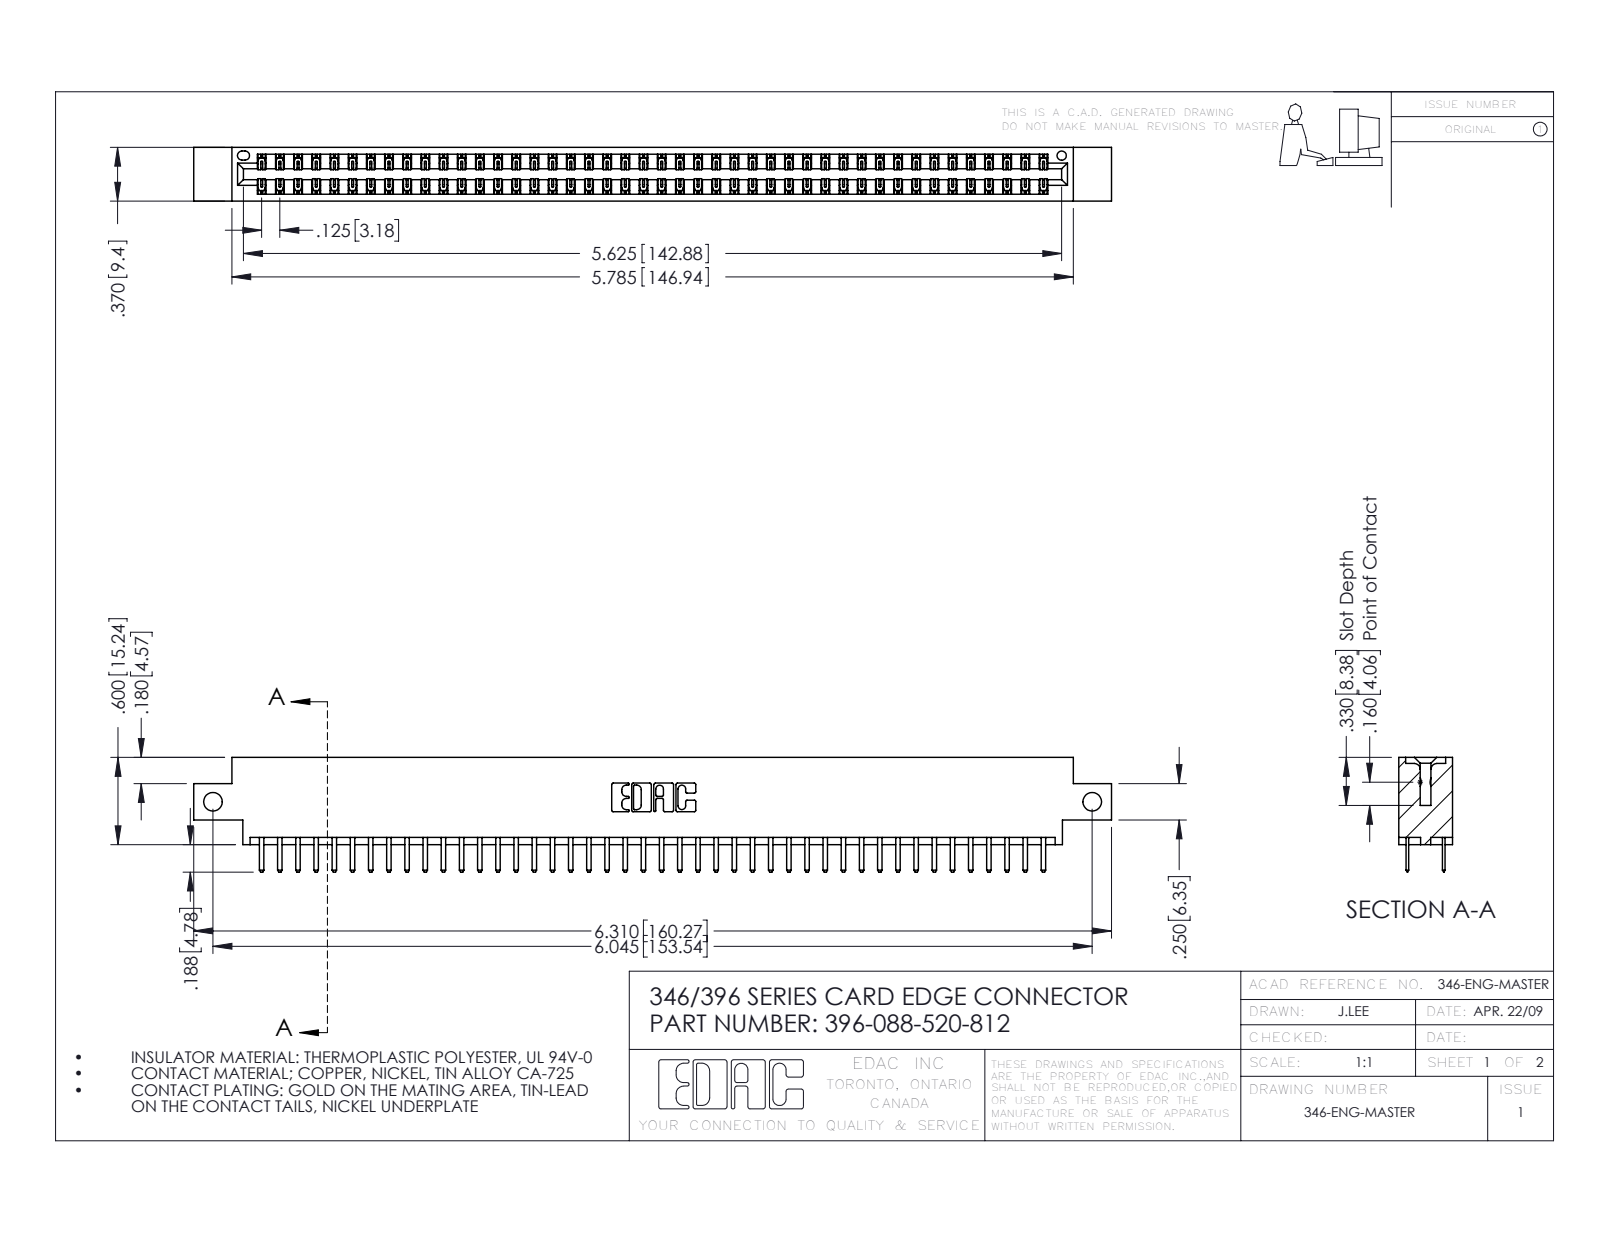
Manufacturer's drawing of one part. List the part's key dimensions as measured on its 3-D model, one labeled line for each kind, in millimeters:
Part name (STEP PRODUCT): 345-292-001_345-293-120; 346 Part_0.170 Offset - Side Mount; 396-088-520-812
STEP written by: SolidWorks 2016 (CONFIG_CONTROL_DESIGN)
Units: millimetres
Bodies: 89 solids, 5054 faces (3336 planar, 1718 cylindrical, 0 other)
Overall size (bounding box): 160.3 × 20 × 9.4
Volume: 15 400 mm³ · Surface area: 21 100 mm²
Round holes (diameter × count): ⌀3.3 ×2, ⌀1.6 ×1
Partial cylindrical surfaces — rounded edges, fillets, slot ends (radius × count): R0.2 ×132, R0.3 ×92, R0.3 ×22, R0.2 ×6, R0.8 ×6, R0.7 ×3, R0.4 ×2, R0.6 ×2
Main face-to-face distances: 1.2, 8.2, 6.4, 9.4, 7, 1.8, 7.6, 0.6, 3.8, 5.6
Hole centre spacings: 153.5
